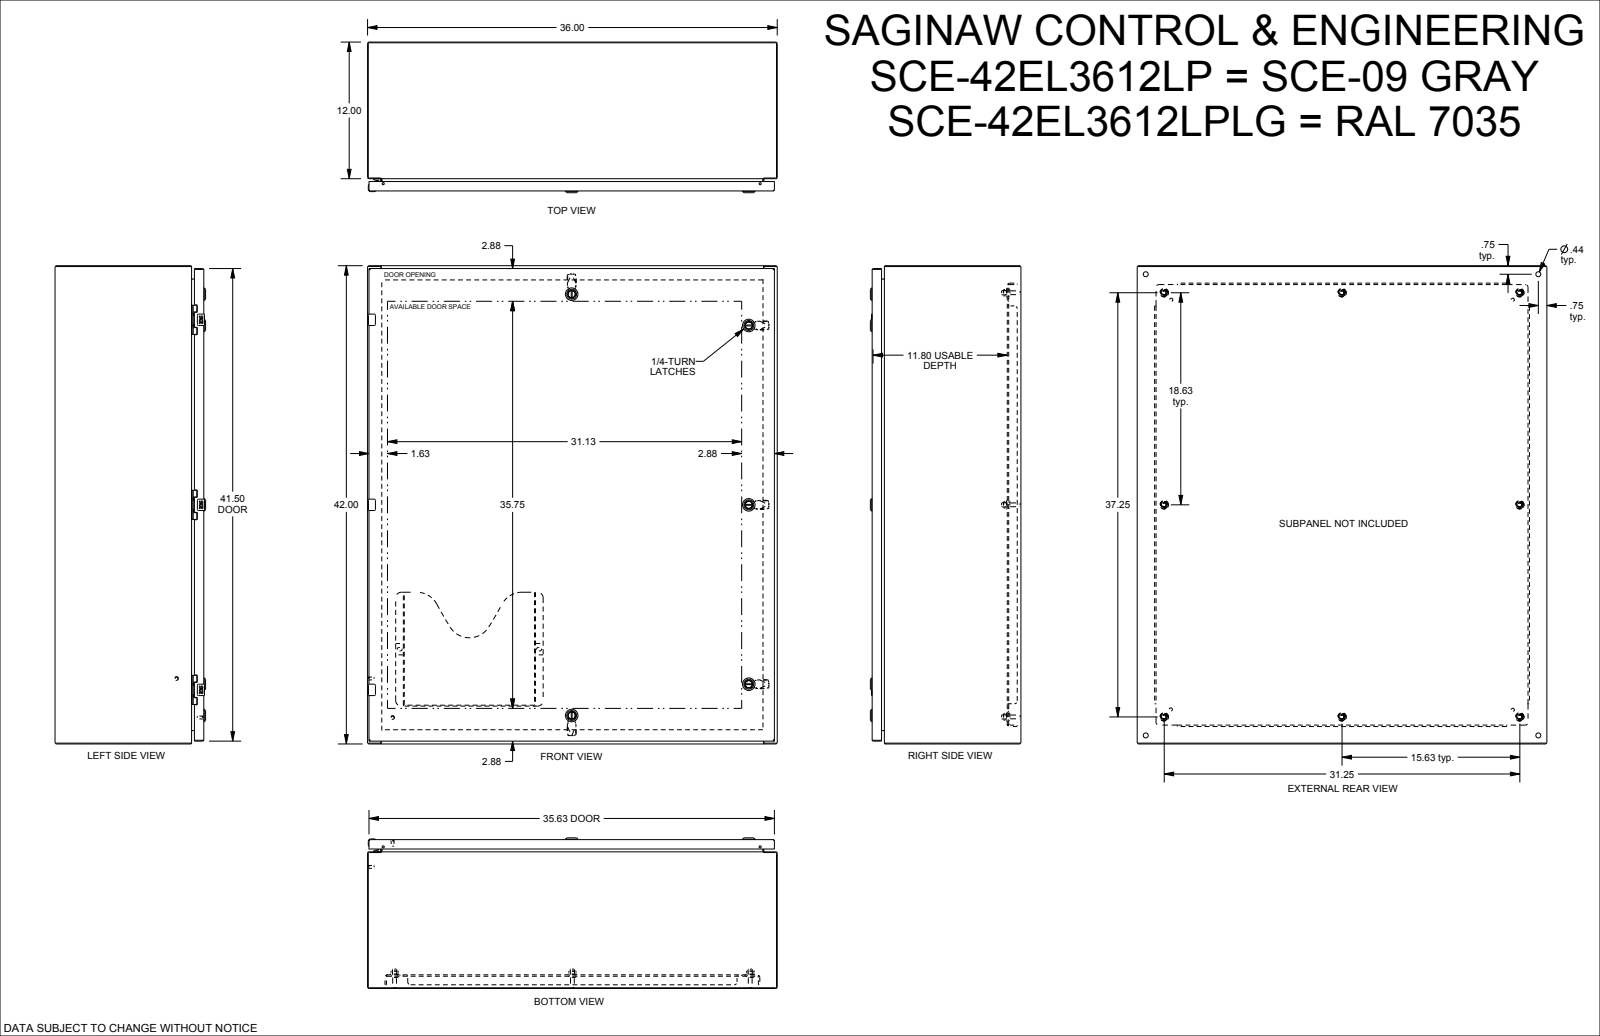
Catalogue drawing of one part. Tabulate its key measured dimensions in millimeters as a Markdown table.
| quantity | value |
| --- | --- |
| part name | SCE-42EL3612LPLG |
| STEP written by | SolidWorks 2019 (CONFIG_CONTROL_DESIGN) |
| units | millimeters |
| bodies | 0 solids, 4774 faces (2327 planar, 1328 cylindrical, 1119 other) |
| overall size | 1066.8 × 914.4 × 336 |
| round holes (diameter × count) | 9.3 × 8, 12.7 × 8, 4.4 × 6, 5.2 × 6, 6.2 × 6, 6.8 × 6, 9.5 × 6, 5 × 5, 8 × 5, 10 × 5, 16.1 × 5, 7.1 × 4 |
| round bosses / shafts (diameter × count) | 4.3 × 9, 9.3 × 8, 8.4 × 8, 6.4 × 6, 6.1 × 6, 28 × 5, 22 × 5, 20.4 × 5 |
| partial cylindrical surfaces (radius × count) | 0.3 × 136, 0.3 × 52, 0.5 × 52, 0.4 × 32, 4 × 20, 1 × 17, 0.6 × 16, 2.5 × 16 |
| main face-to-face distances | 1.9, 1.9, 328.2, 330.1, 332.1, 330.1, 30.5, 301.6, 25.4, 28.6 |
| hole center spacings | 412.8, 25, 825.5, 0.5, 12.5, 12.5, 114.1, 387.7 |
